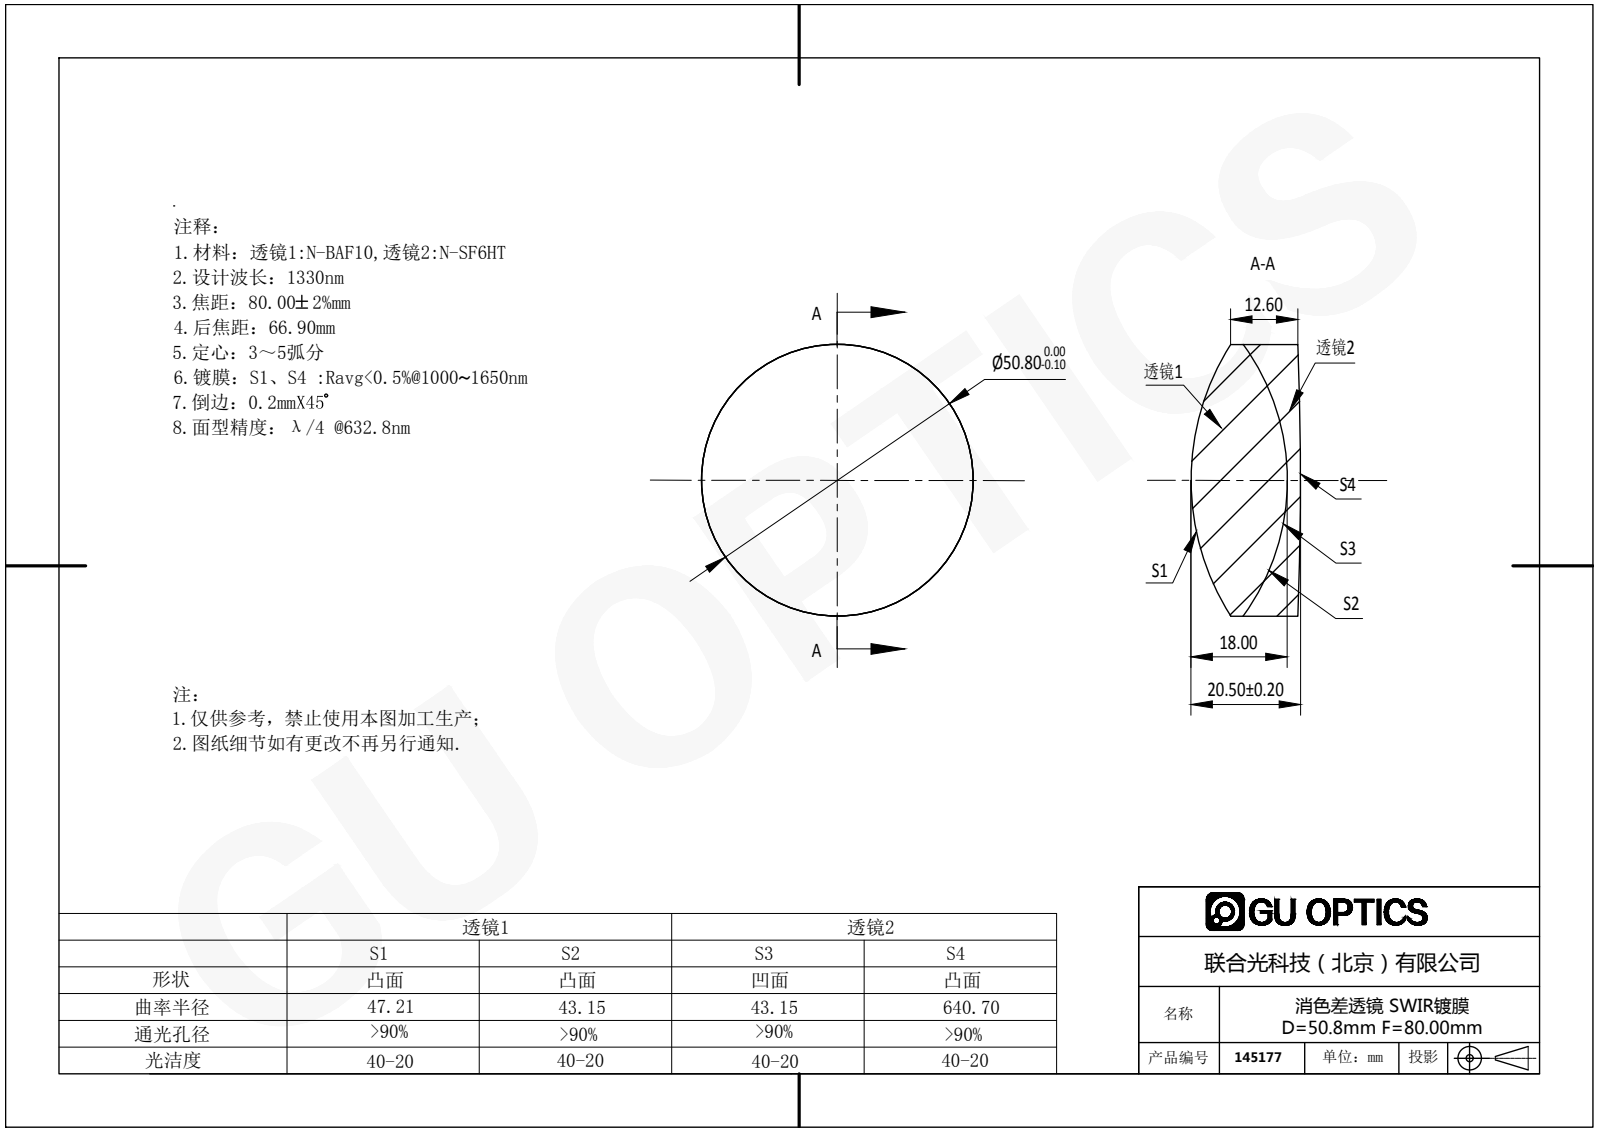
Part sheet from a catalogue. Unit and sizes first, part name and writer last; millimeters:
Units: millimetres
Overall size (bounding box): 50.8 × 50.8 × 20.5
Round bosses / shafts (diameter × count): ⌀50.8 ×1
Volume: 33 738 mm³ · Surface area: 10 718 mm²
Bodies: 2 solids, 12 faces (0 planar, 4 cylindrical, 8 other)
Part name (STEP PRODUCT): 145177
STEP written by: SolidWorks 2016 (AUTOMOTIVE_DESIGN)
